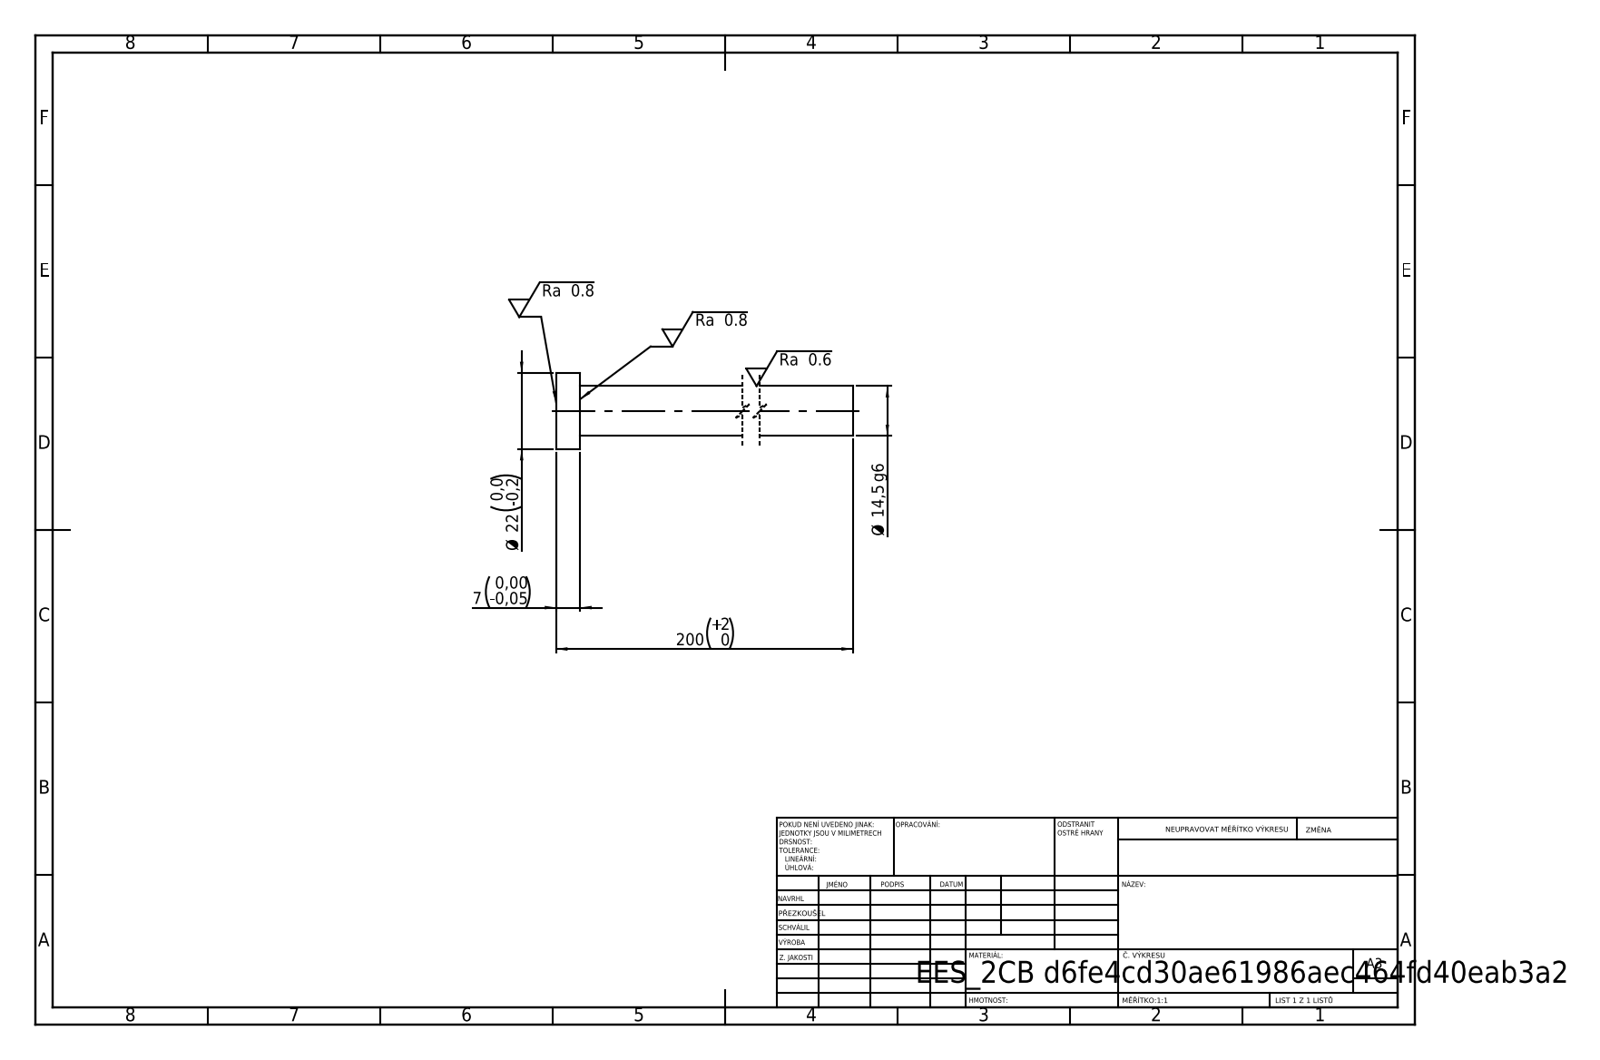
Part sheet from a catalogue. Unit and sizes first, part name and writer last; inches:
Units: inches
Overall size (bounding box): 7.874 × 0.866 × 0.866
Round bosses / shafts (diameter × count): ⌀0.866 ×1, ⌀0.571 ×1
Main face-to-face distances: 0.276, 7.874, 7.598
Volume: 2.107 in³ · Surface area: 15.56 in²
Bodies: 1 solid, 7 faces (3 planar, 4 cylindrical, 0 other)
STEP written by: SolidWorks 2019 (CONFIG_CONTROL_DESIGN)
